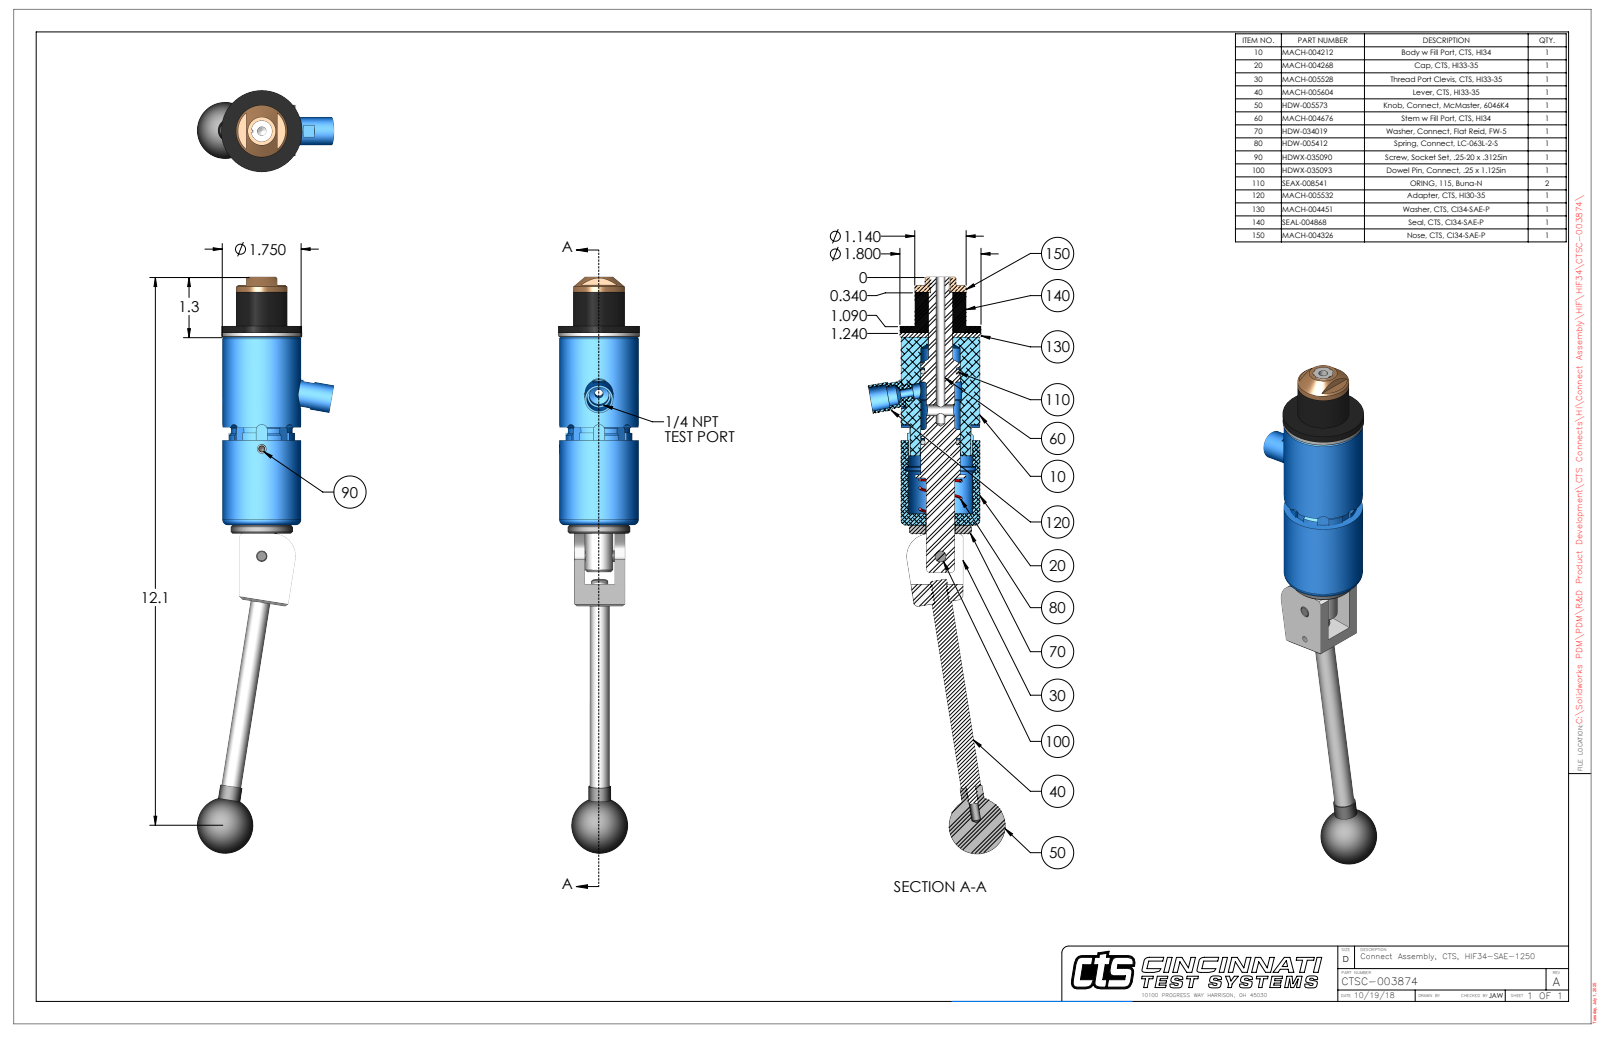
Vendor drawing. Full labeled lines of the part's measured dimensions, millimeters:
Part name (STEP PRODUCT): CTSC-003874
STEP written by: SolidWorks 2023 (AUTOMOTIVE_DESIGN)
Units: millimetres
Bodies: 9 solids, 328 faces (120 planar, 139 cylindrical, 69 other)
Overall size (bounding box): 324.4 × 77.3 × 45.7
Volume: 241 100 mm³ · Surface area: 54 910 mm²
Round holes (diameter × count): ⌀5.1 ×2, ⌀3.8 ×1, ⌀4.7 ×1, ⌀5.2 ×1, ⌀6.3 ×1, ⌀6.4 ×1, ⌀6.4 ×1, ⌀8 ×1, ⌀10.7 ×1, ⌀11.1 ×1, ⌀13.5 ×1, ⌀13.7 ×1
Round bosses / shafts (diameter × count): ⌀12.7 ×2, ⌀11.2 ×2, ⌀6.4 ×2, ⌀45.7 ×1, ⌀44.5 ×1, ⌀35.1 ×1, ⌀29 ×1, ⌀15.9 ×1
Partial cylindrical surfaces — rounded edges, fillets, slot ends (radius × count): R3.2 ×4, R0.7 ×2, R4.2 ×1, R4.2 ×1, R4.4 ×1, R8.4 ×1, R12.7 ×1, R17.7 ×1
Main face-to-face distances: 2.4, 108.2, 105.8, 22.9, 25.2, 131, 28.4, 19.1, 3.8, 6.2
Hole centre spacings: 18.8, 60.4, 79.1
